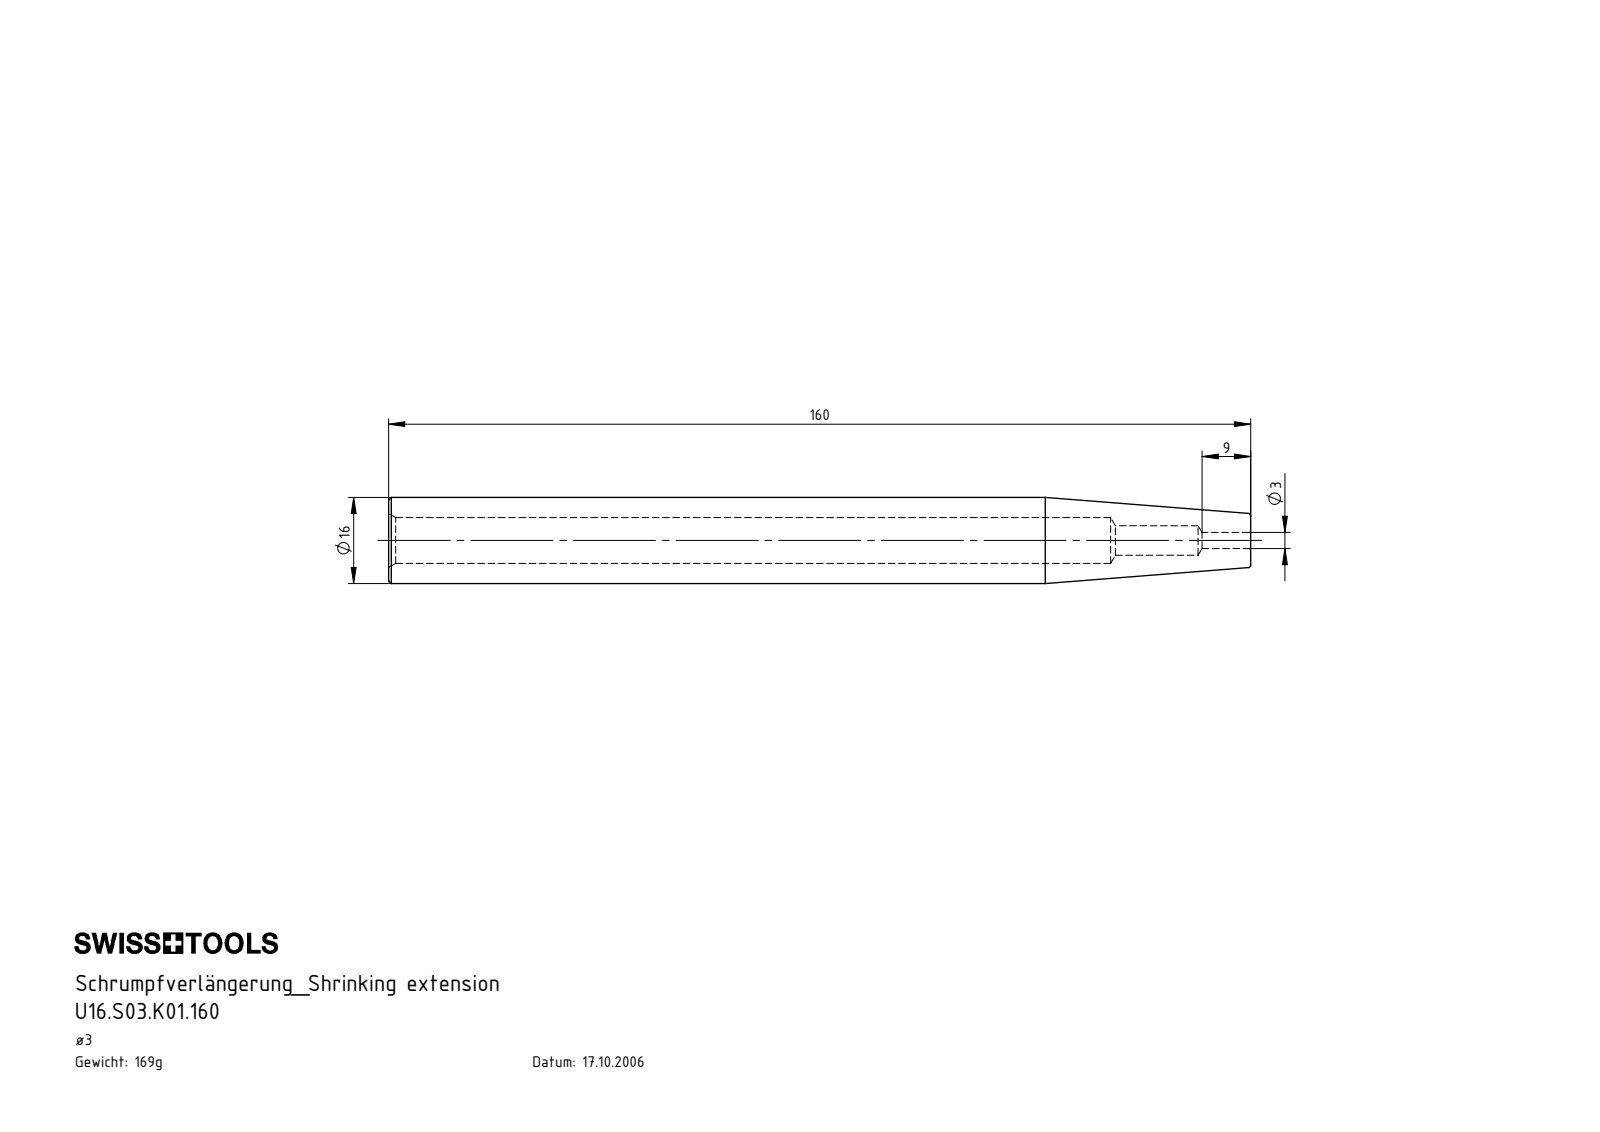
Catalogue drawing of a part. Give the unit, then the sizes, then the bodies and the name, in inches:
Units: inches
Overall size (bounding box): 6.299 × 0.63 × 0.63
Round holes (diameter × count): ⌀0.118 ×1, ⌀0.217 ×1, ⌀0.335 ×1
Round bosses / shafts (diameter × count): ⌀0.63 ×1
Main face-to-face distances: 6.299
Volume: 1.315 in³ · Surface area: 18.37 in²
Bodies: 1 solid, 24 faces (2 planar, 8 cylindrical, 14 other)
Part name (STEP PRODUCT): U16.S03.K01.160
STEP written by: SolidWorks 2017 (AUTOMOTIVE_DESIGN)
